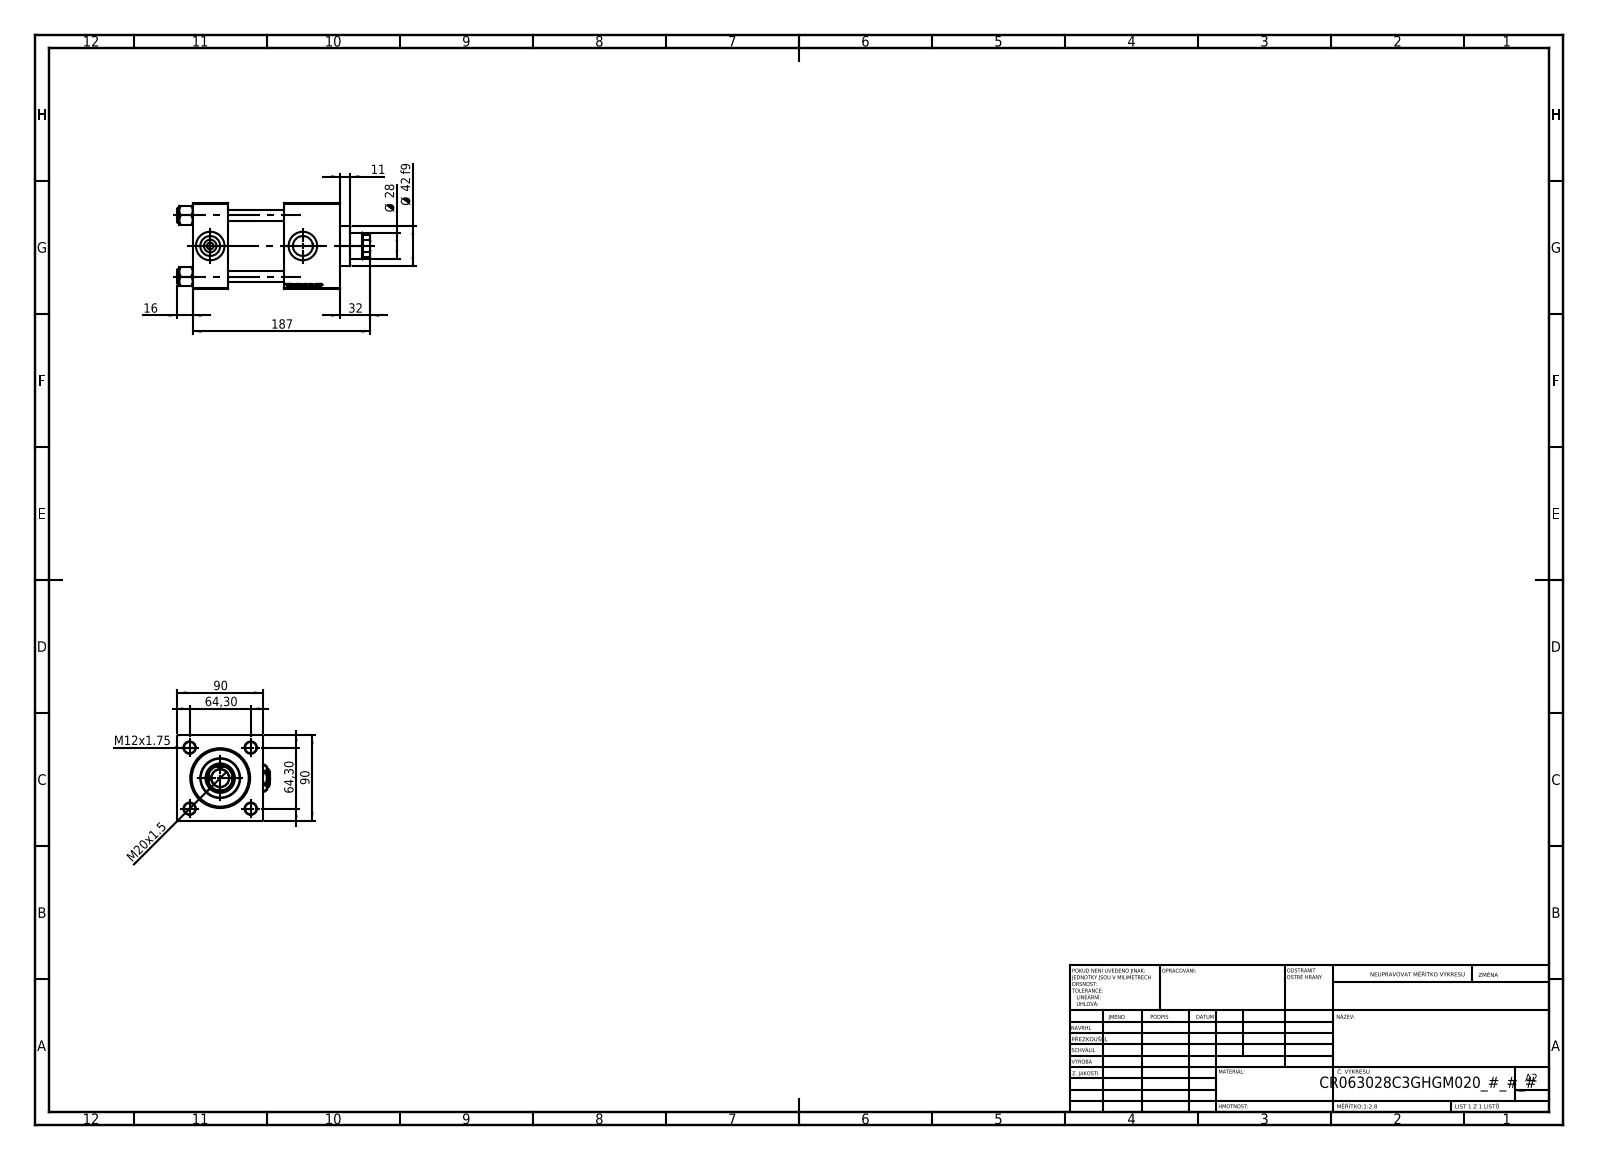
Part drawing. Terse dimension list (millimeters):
name: NUT_M5_C; V215CR_C_Body; V215CR_VCP_C; V215_VC_A (+2 more)
written by: SolidWorks 2019 (CONFIG_CONTROL_DESIGN)
unit: mm
bodies: 13 solids, 1250 faces (574 planar, 98 cylindrical, 578 other)
size: 203 × 97 × 90
volume: 940 483 mm³; area: 183 915 mm²
holes: 4× ⌀12, 2× ⌀7, 2× ⌀20.96, 2× ⌀30, 1× ⌀18.5, 1× ⌀28, 1× ⌀31, 1× ⌀50, 1× ⌀60, 1× ⌀63
bosses: 4× ⌀15, 1× ⌀69, 1× ⌀42
rounds: 1× R13.5
face distances: 90, 59, 37, 118, 155, 96, 126.3, 89.3, 30.3, 28.7
hole spacings: 45.47, 64.3, 90.93, 97.5
